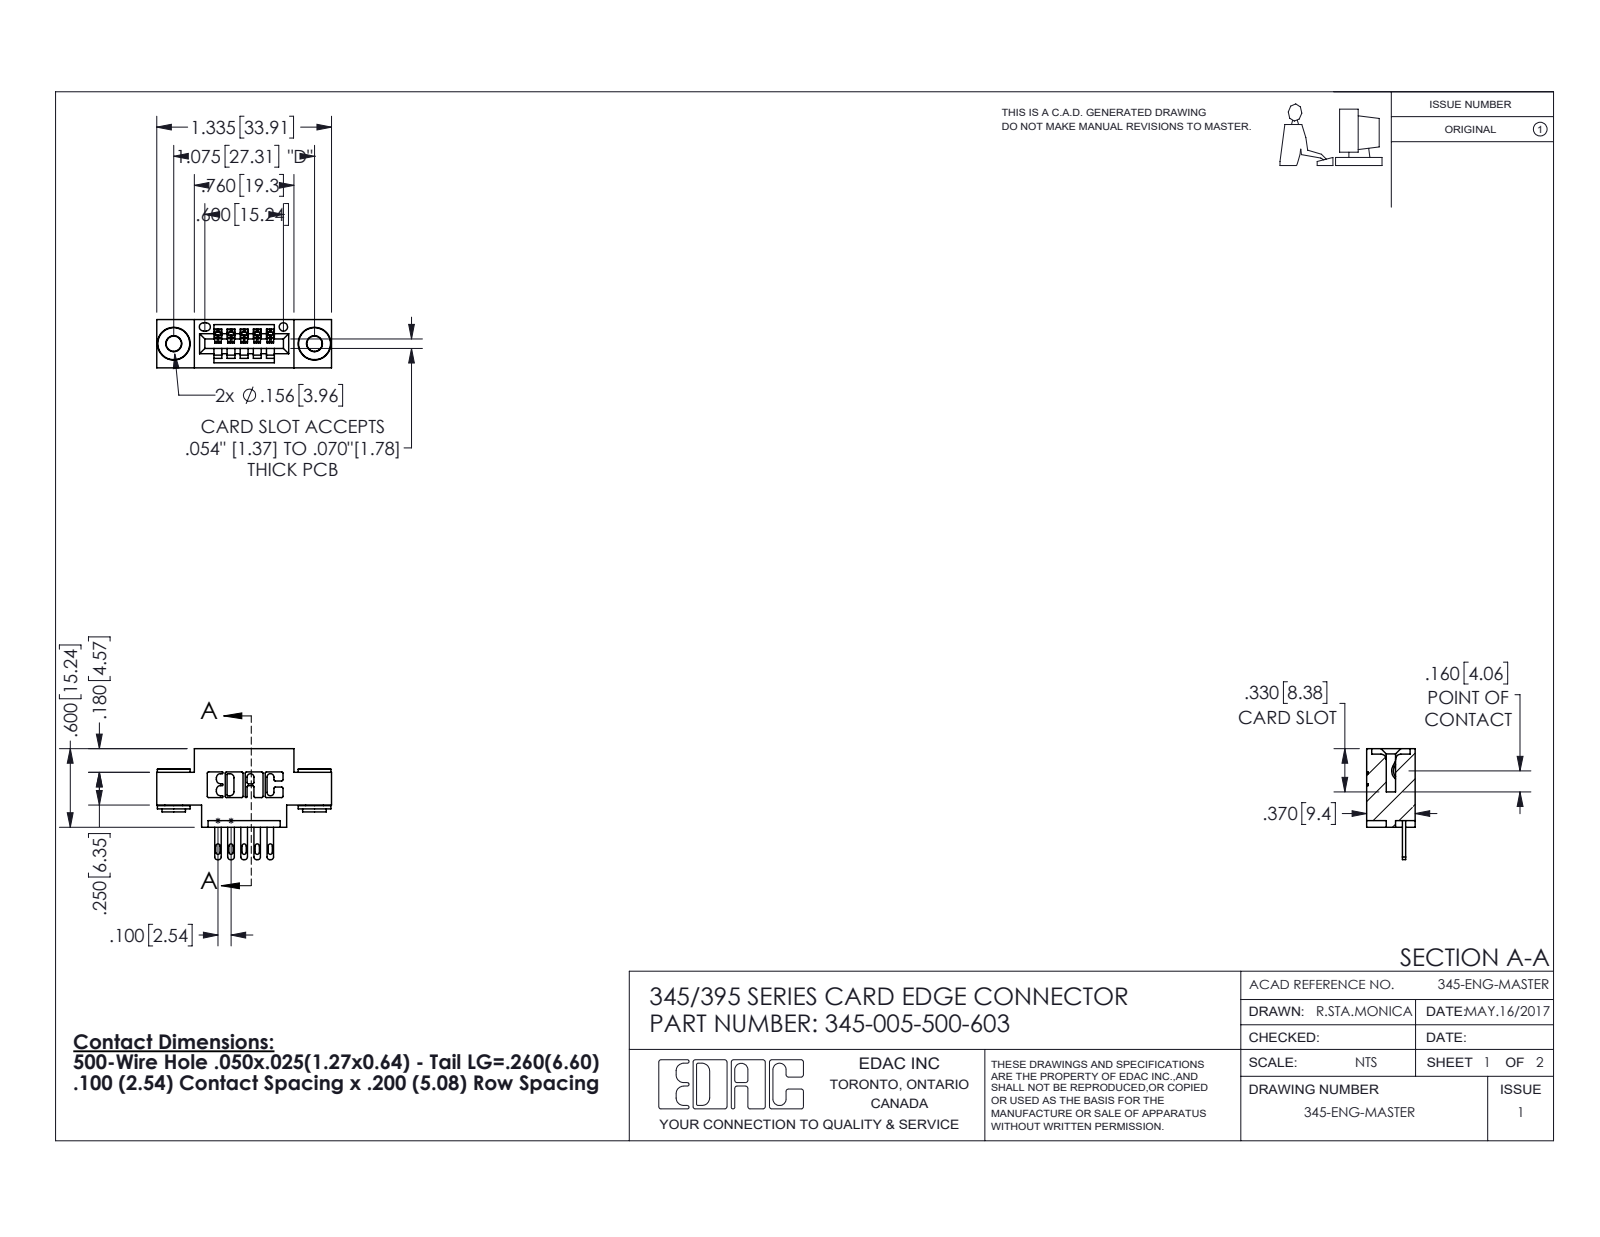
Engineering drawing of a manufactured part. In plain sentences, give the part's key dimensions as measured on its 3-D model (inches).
The part is named "345-292-001_345-293-100; 345 Part_0.170 Offset - 0.156 Dia-TH; 345-250-002_345-250-002-102; 345-005-500-603". Its 3-D file was written by "SolidWorks 2016 (CONFIG_CONTROL_DESIGN)". It is 8 solids with 438 faces: 264 planar, 166 cylindrical and 8 other. Overall it measures 1.335 by 0.847 by 0.37 inches. Its volume is 0.172 cubic inches and its surface area 5.589 square inches. Round holes: 2 of diameter 0.116, 2 of diameter 0.156, 1 of diameter 0.064. Round bosses or shafts: 2 of diameter 0.25, 2 of diameter 0.18, 2 of diameter 0.136. Partial cylindrical surfaces (rounded edges, fillets, slot ends): 22 of radius 0.01, 10 of radius 0.006, 10 of radius 0.016, 10 of radius 0.02, 6 of radius 0.007, 6 of radius 0.031, 3 of radius 0.026, 2 of radius 0.031. The main face-to-face distances are 0.37, 0.2, 0.1, 0.072, 0.298, 0.25, 0.025, 0.098, 0.272, 0.06. The hole center spacings are 0.27, 0.847, 1.075.
